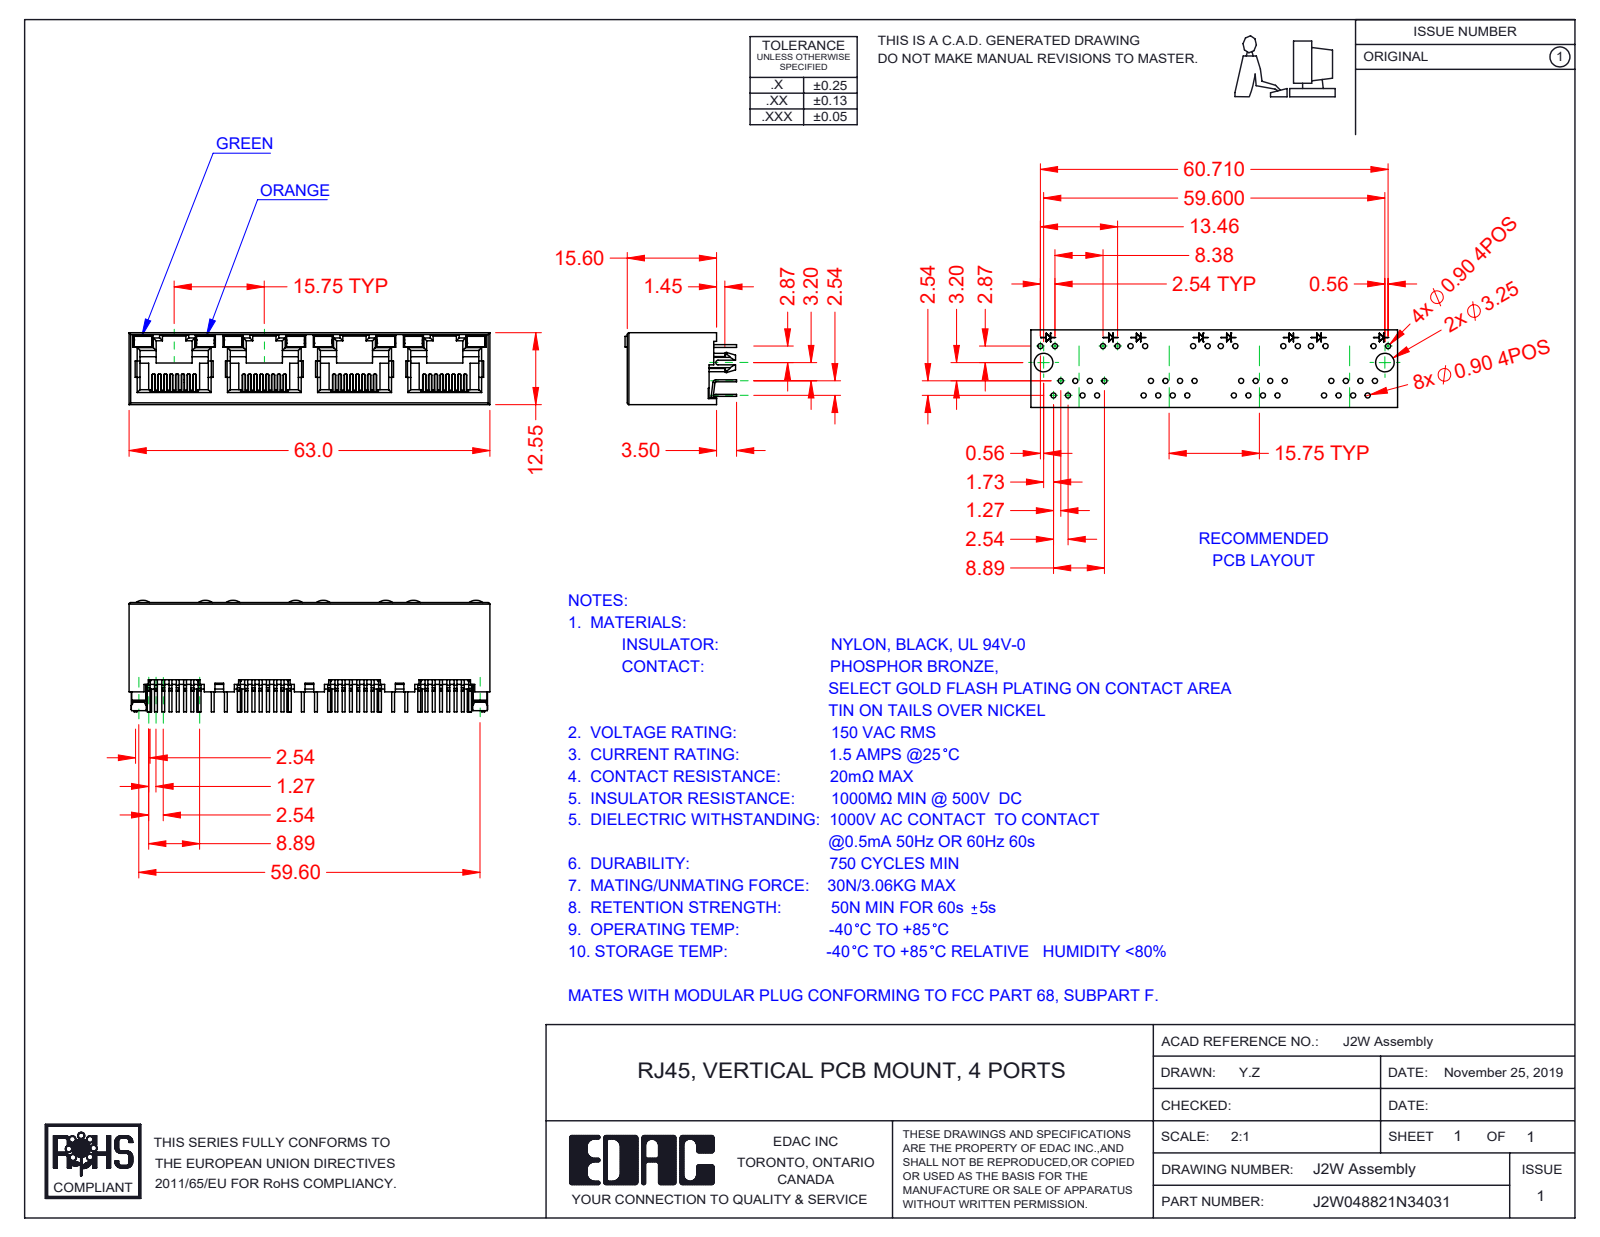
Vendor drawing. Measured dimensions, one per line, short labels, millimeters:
name: J2W048821N34031; 2W Contact Lock; 2W LED RH_4-Orange; 2W Insulator (+2 more)
written by: SolidWorks 2020 (CONFIG_CONTROL_DESIGN)
unit: mm
bodies: 45 solids, 3135 faces (2600 planar, 477 cylindrical, 58 other)
size: 63 × 19.5 × 12.55
volume: 5 335 mm³; area: 13 144 mm²
rounds: 64× R0.15, 29× R0.2, 28× R0.5, 14× R0.3, 8× R0.45, 8× R2, 2× R0.25, 2× R1.5
face distances: 12.55, 11.9, 0.65, 15.75, 0.36, 1.5, 0.78, 0.6, 11.3, 31.5
